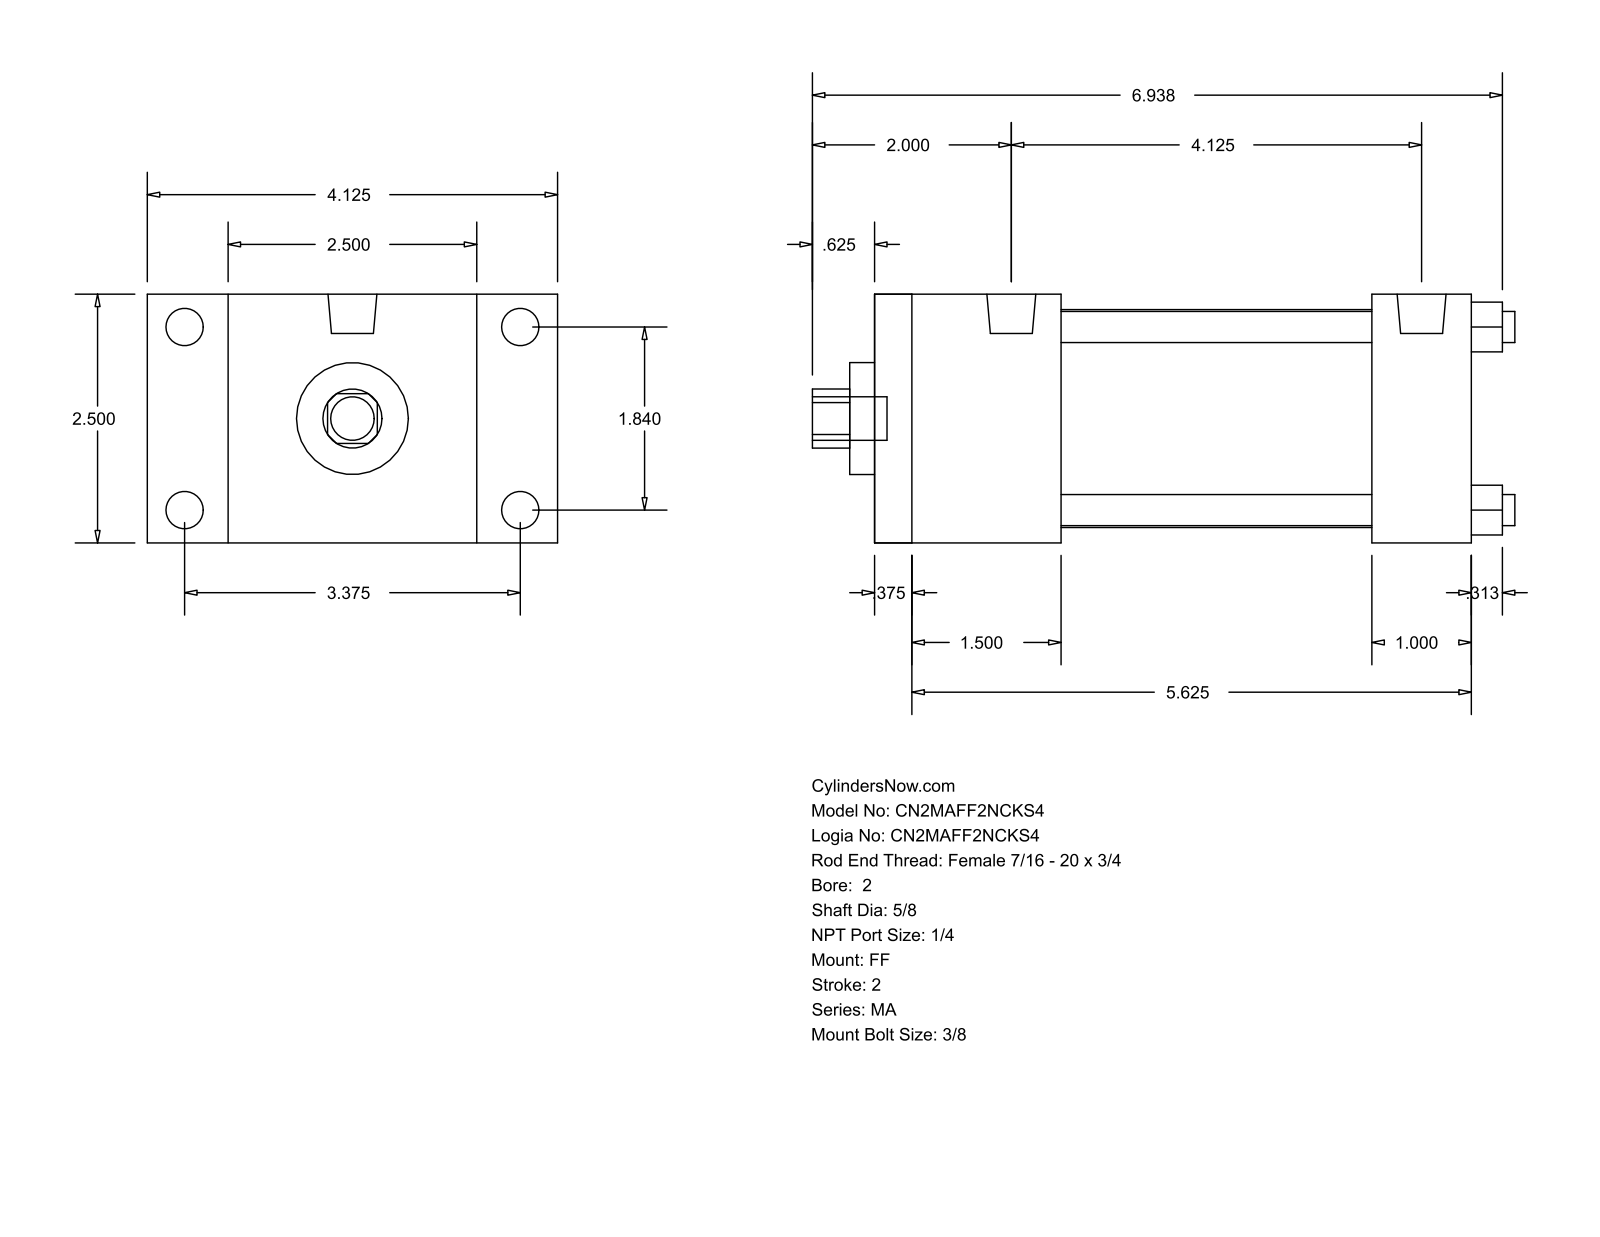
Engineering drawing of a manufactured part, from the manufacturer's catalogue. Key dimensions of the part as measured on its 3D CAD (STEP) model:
Part name (STEP PRODUCT): MA_FF__0200_0.625
STEP written by: GSSL Pune (CONFIG_CONTROL_DESIGN)
Units: millimetres
Bodies: 0 solids, 92 faces (64 planar, 28 cylindrical, 0 other)
Overall size (bounding box): 179.39 × 104.78 × 63.5
Round holes (diameter × count): ⌀7.94 ×4, ⌀15.88 ×1, ⌀28.57 ×1, ⌀55.63 ×1
Round bosses / shafts (diameter × count): ⌀9.53 ×4, ⌀7.94 ×4, ⌀12.49 ×2, ⌀11.11 ×1
Partial cylindrical surfaces — rounded edges, fillets, slot ends (radius × count): R7.54 ×1
Main face-to-face distances: 63.5, 152.4, 9.52, 142.88, 104.78, 25.4, 38.1, 47.62, 127, 117.48
Hole centre spacings: 33.05, 46.74, 66.1
